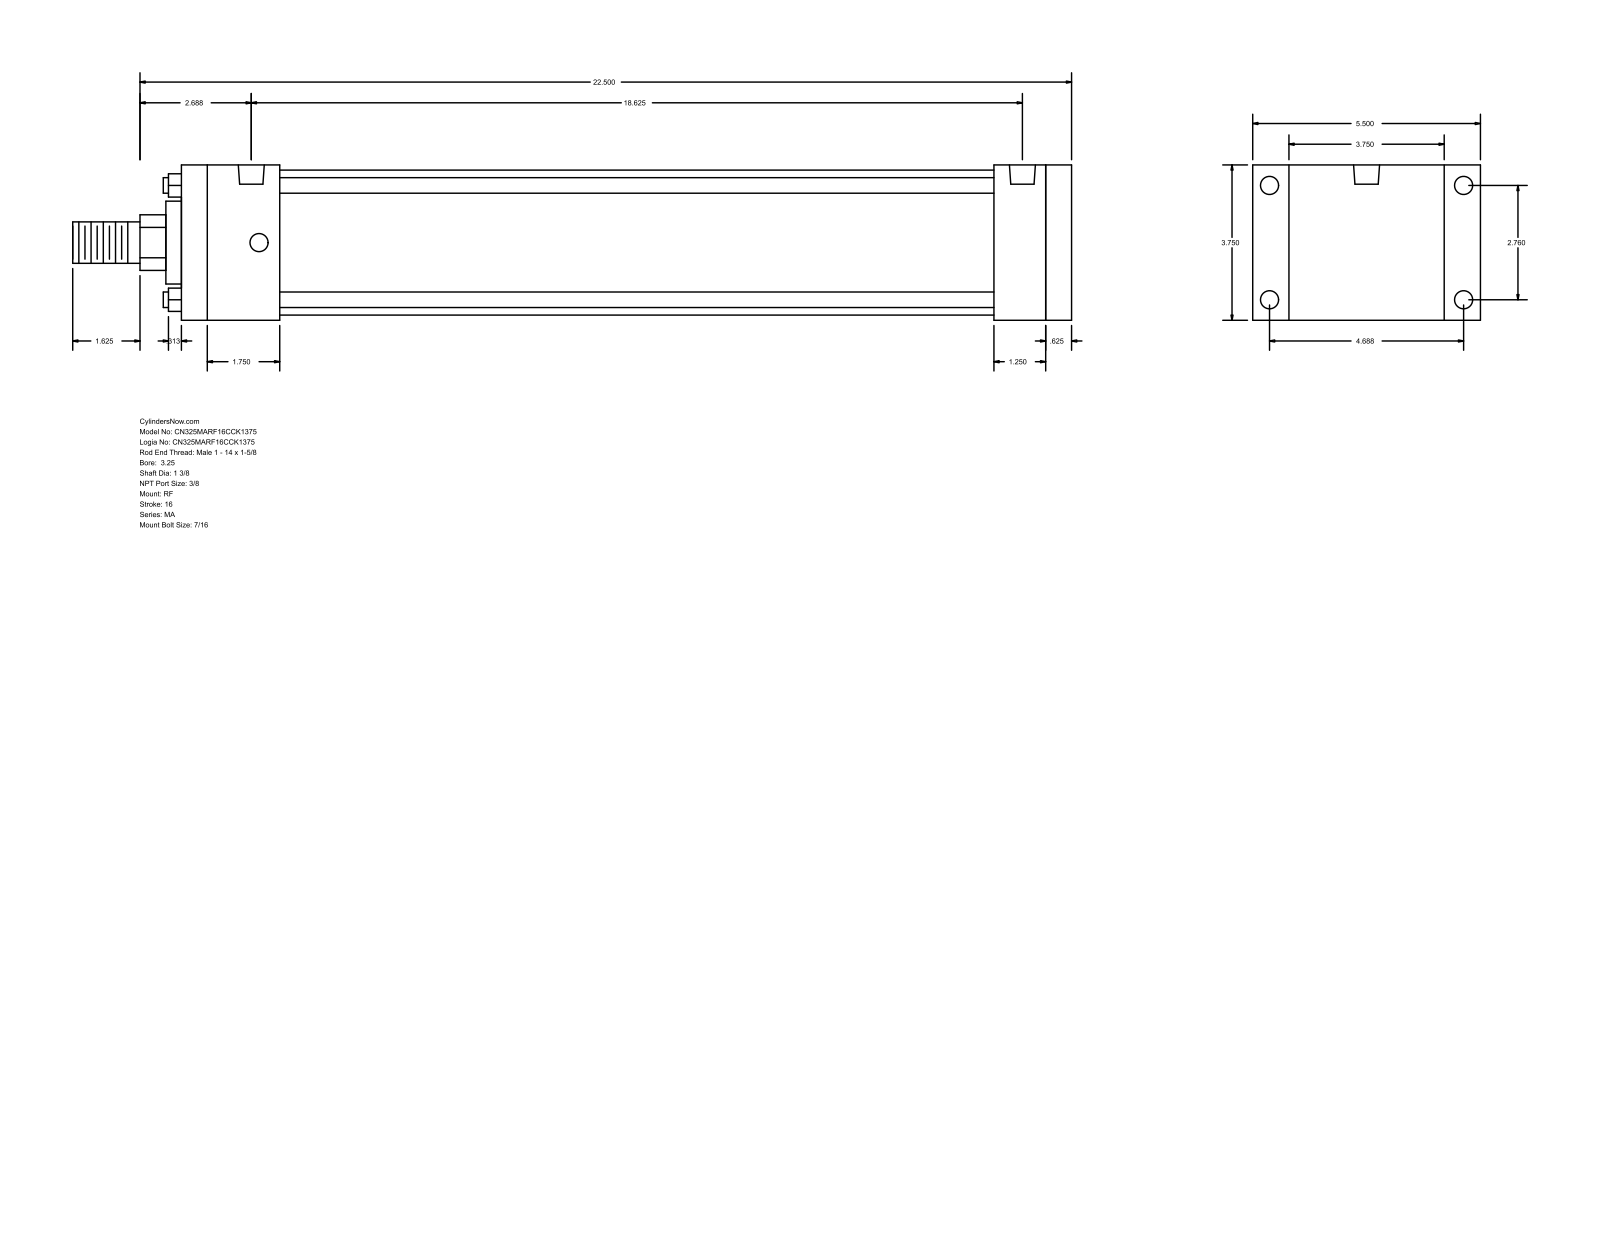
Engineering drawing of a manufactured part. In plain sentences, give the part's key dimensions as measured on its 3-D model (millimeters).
The part is named "MA_RF__0325_1.375". Its 3-D file was written by "GSSL Pune (CONFIG_CONTROL_DESIGN)". It is 0 solids with 92 faces: 64 planar, 28 cylindrical and 0 other. Overall it measures 612.77 by 139.7 by 95.25 millimeters. Round holes: 8 of diameter 11.11, 2 of diameter 15.93. Round bosses or shafts: 4 of diameter 9.53, 1 of diameter 88.9, 1 of diameter 50.8, 1 of diameter 34.92, 1 of diameter 25.4. Partial cylindrical surfaces (rounded edges, fillets, slot ends): 1 of radius 17.06. The main face-to-face distances are 95.24, 546.1, 15.88, 530.22, 22.23, 117.47, 498.48, 31.74, 47.62, 60.32. The hole center spacings are 70.1, 119.06, 138.16, 463.55, 4.76, 4.77, 468.31, 468.32.
